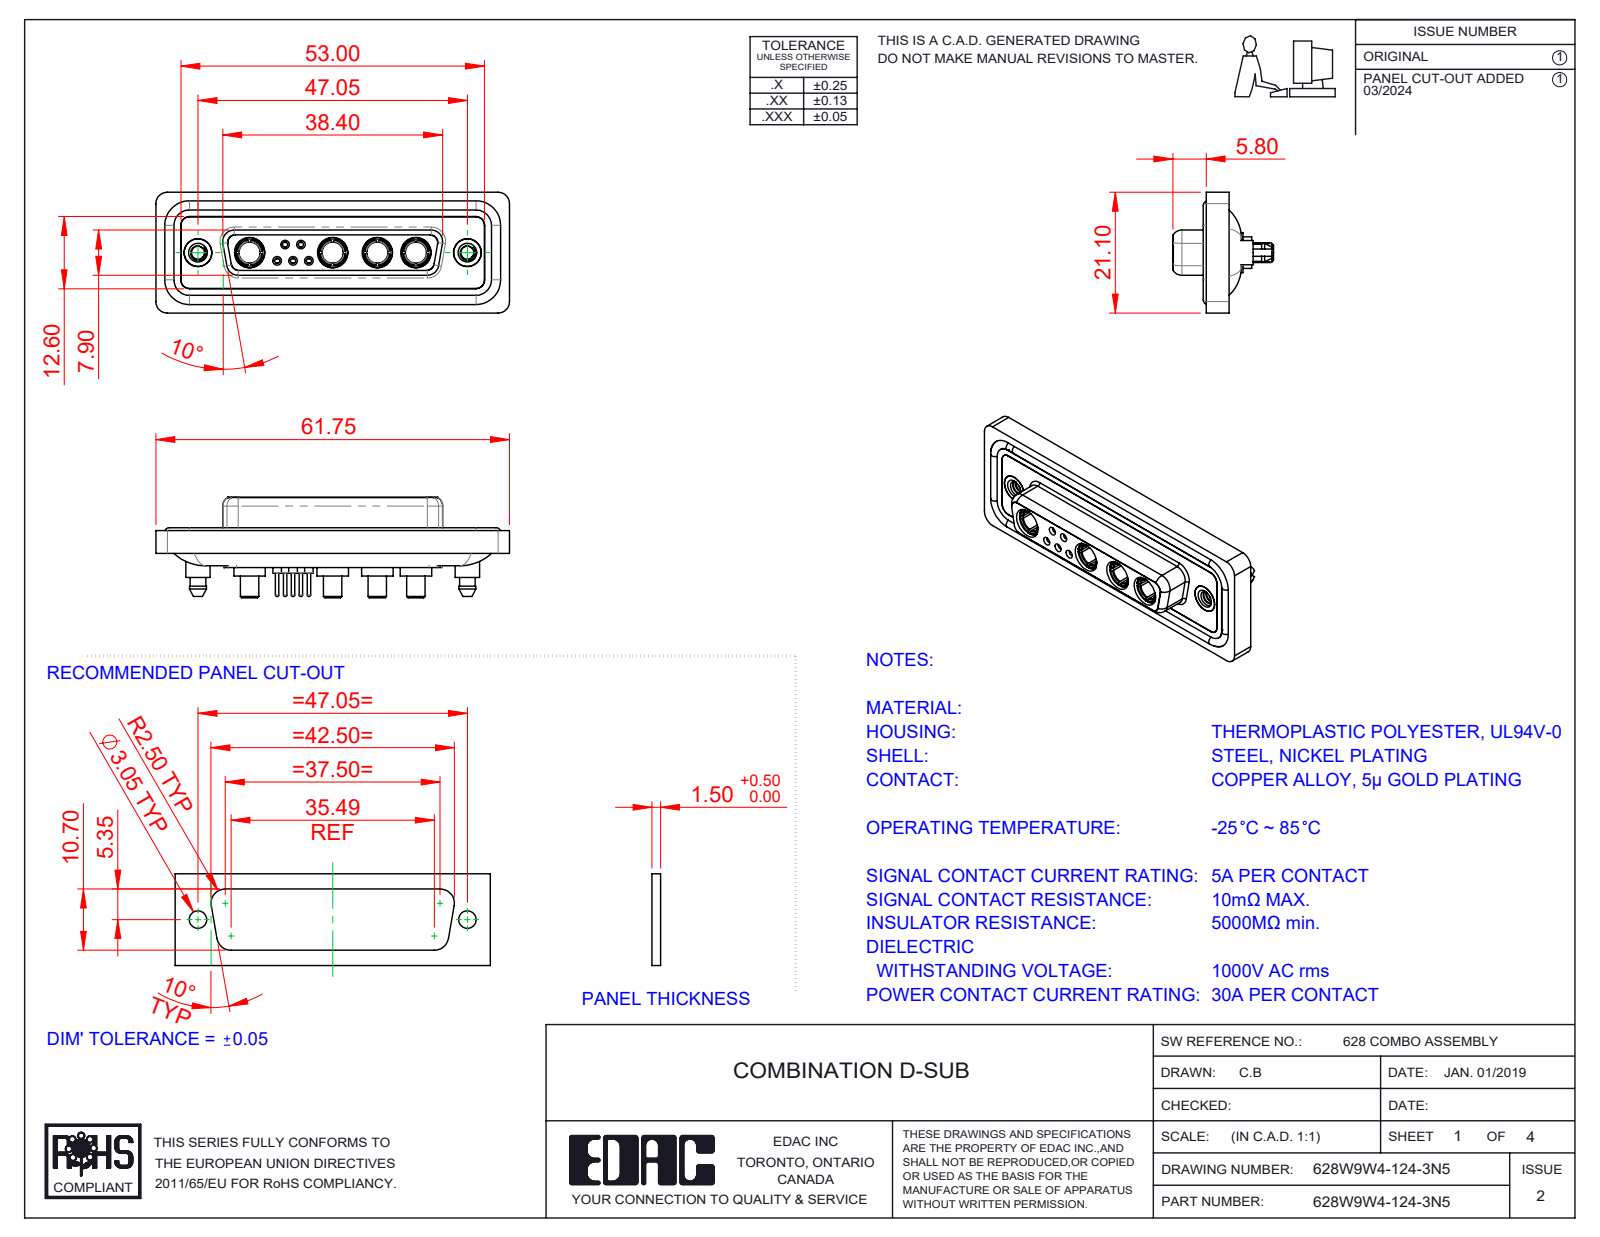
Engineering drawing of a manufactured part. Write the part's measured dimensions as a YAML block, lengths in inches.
part_name: "Power Socket_30A S; 628Combo Contact Row 1_24; 628Combo Shell Front_25 Contacts; 628W9W4-124-3N5 (+5 more)"
step_written_by: "SolidWorks 2023 (CONFIG_CONTROL_DESIGN)"
units: inches
bodies: {solids: 20, faces: 1007, planar: 312, cylindrical: 407, other: 288}
overall_size: [2.431, 0.831, 0.691]
volume: 0.512
surface_area: 21.57
round_holes:
  - {diameter: 0.191, count: 6}
  - {diameter: 0.035, count: 5}
  - {diameter: 0.043, count: 5}
  - {diameter: 0.059, count: 5}
  - {diameter: 0.079, count: 5}
  - {diameter: 0.146, count: 4}
  - {diameter: 0.209, count: 4}
  - {diameter: 0.063, count: 3}
  - {diameter: 0.067, count: 2}
  - {diameter: 0.089, count: 2}
  - {diameter: 0.157, count: 2}
  - {diameter: 0.159, count: 2}
round_bosses_or_shafts:
  - {diameter: 0.063, count: 6}
  - {diameter: 0.087, count: 5}
  - {diameter: 0.024, count: 5}
  - {diameter: 0.217, count: 4}
  - {diameter: 0.205, count: 4}
  - {diameter: 0.195, count: 4}
  - {diameter: 0.187, count: 4}
  - {diameter: 0.148, count: 4}
partial_cylinders:
  - {radius: 0.059, count: 24}
  - {radius: 0.079, count: 18}
  - {radius: 0.063, count: 10}
  - {radius: 0.053, count: 8}
  - {radius: 0.01, count: 4}
  - {radius: 0.02, count: 4}
  - {radius: 0.024, count: 4}
  - {radius: 0.026, count: 4}
face_to_face_distances: [0.016, 0.071, 0.293, 0.222, 0.02, 0.278, 0.26, 0.063, 0.043, 0.114]
hole_center_spacings: [0.124, 0.109, 0.198, 0.109, 0.173, 0.198, 0.218, 0.226]
